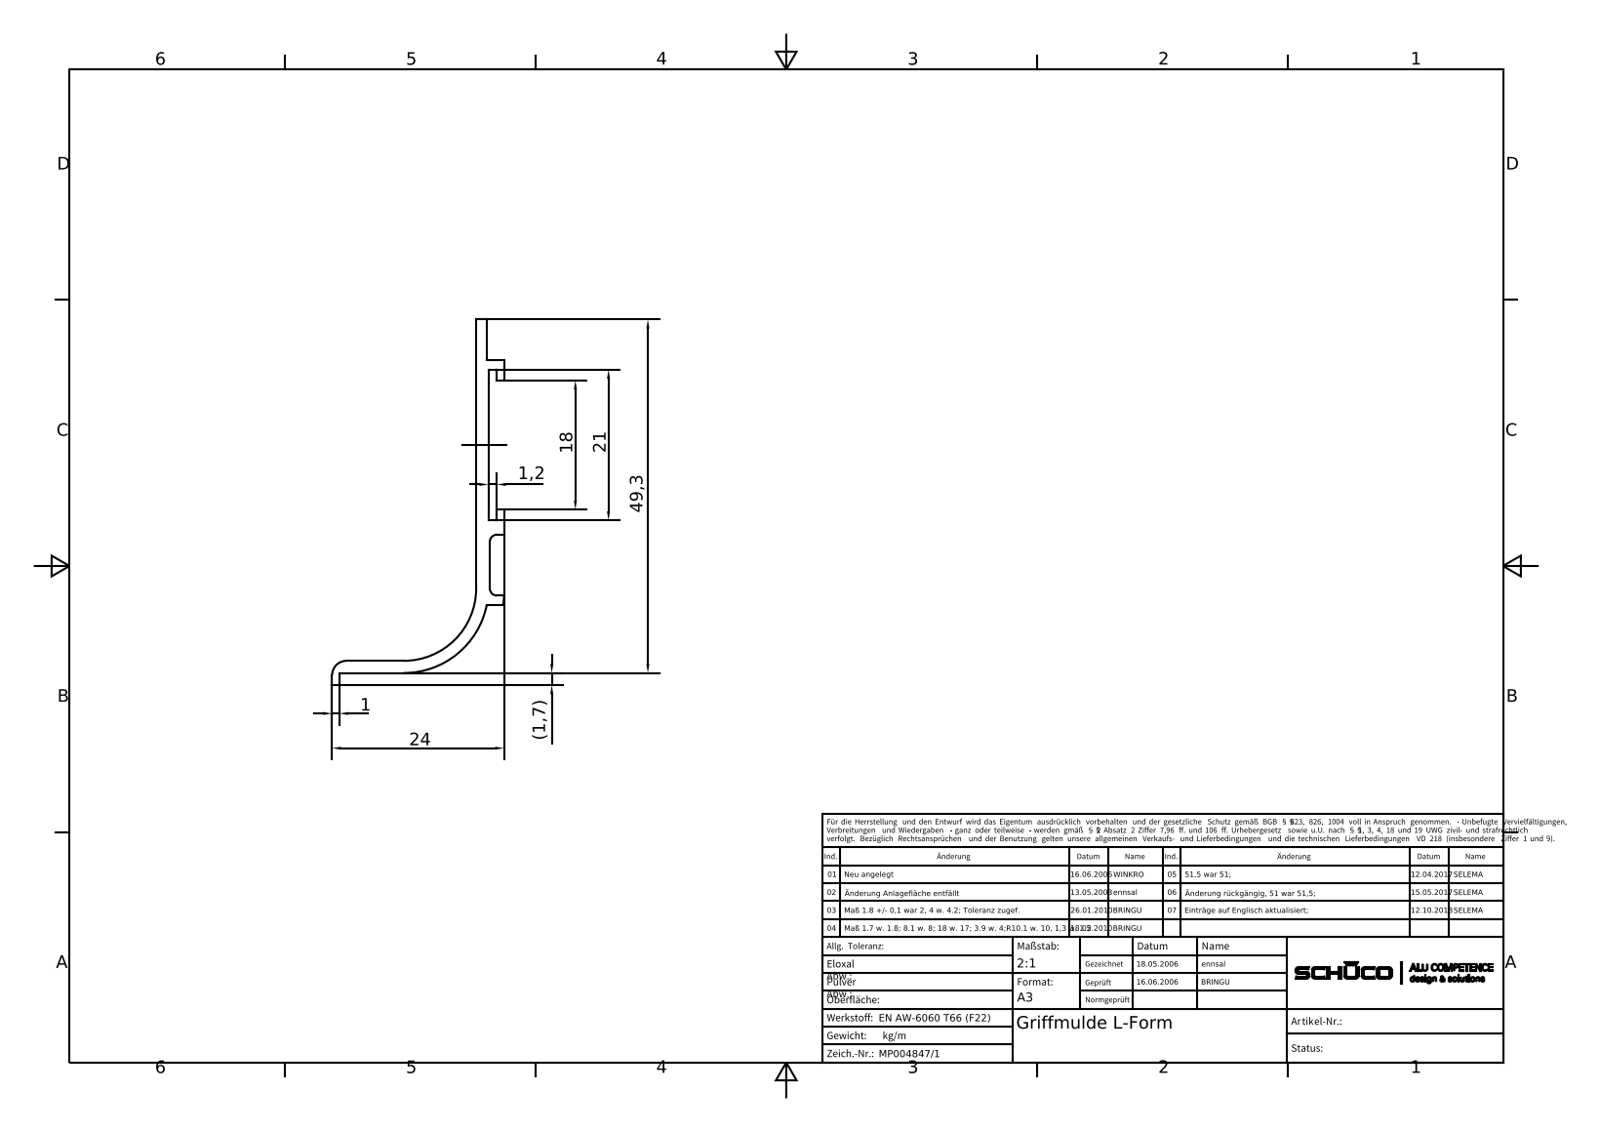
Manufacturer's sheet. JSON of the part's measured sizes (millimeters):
{"part_name": "MP00484701", "step_written_by": "Autodesk Inventor 2015 (AUTOMOTIVE_DESIGN)", "units": "millimeters", "bodies": {"solids": 1, "faces": 30, "planar": 24, "cylindrical": 6, "other": 0}, "overall_size": [51, 24, 10], "volume_mm3": 1250, "surface_area_mm2": 1784, "partial_cylinders_radius": [[1, 2], [2, 1], [10.1, 1], [11.8, 1], [12, 1]], "face_to_face_distances": [1.7, 10, 1.5, 1, 2, 1.9, 3.9, 2.2, 0.4, 2.4]}
